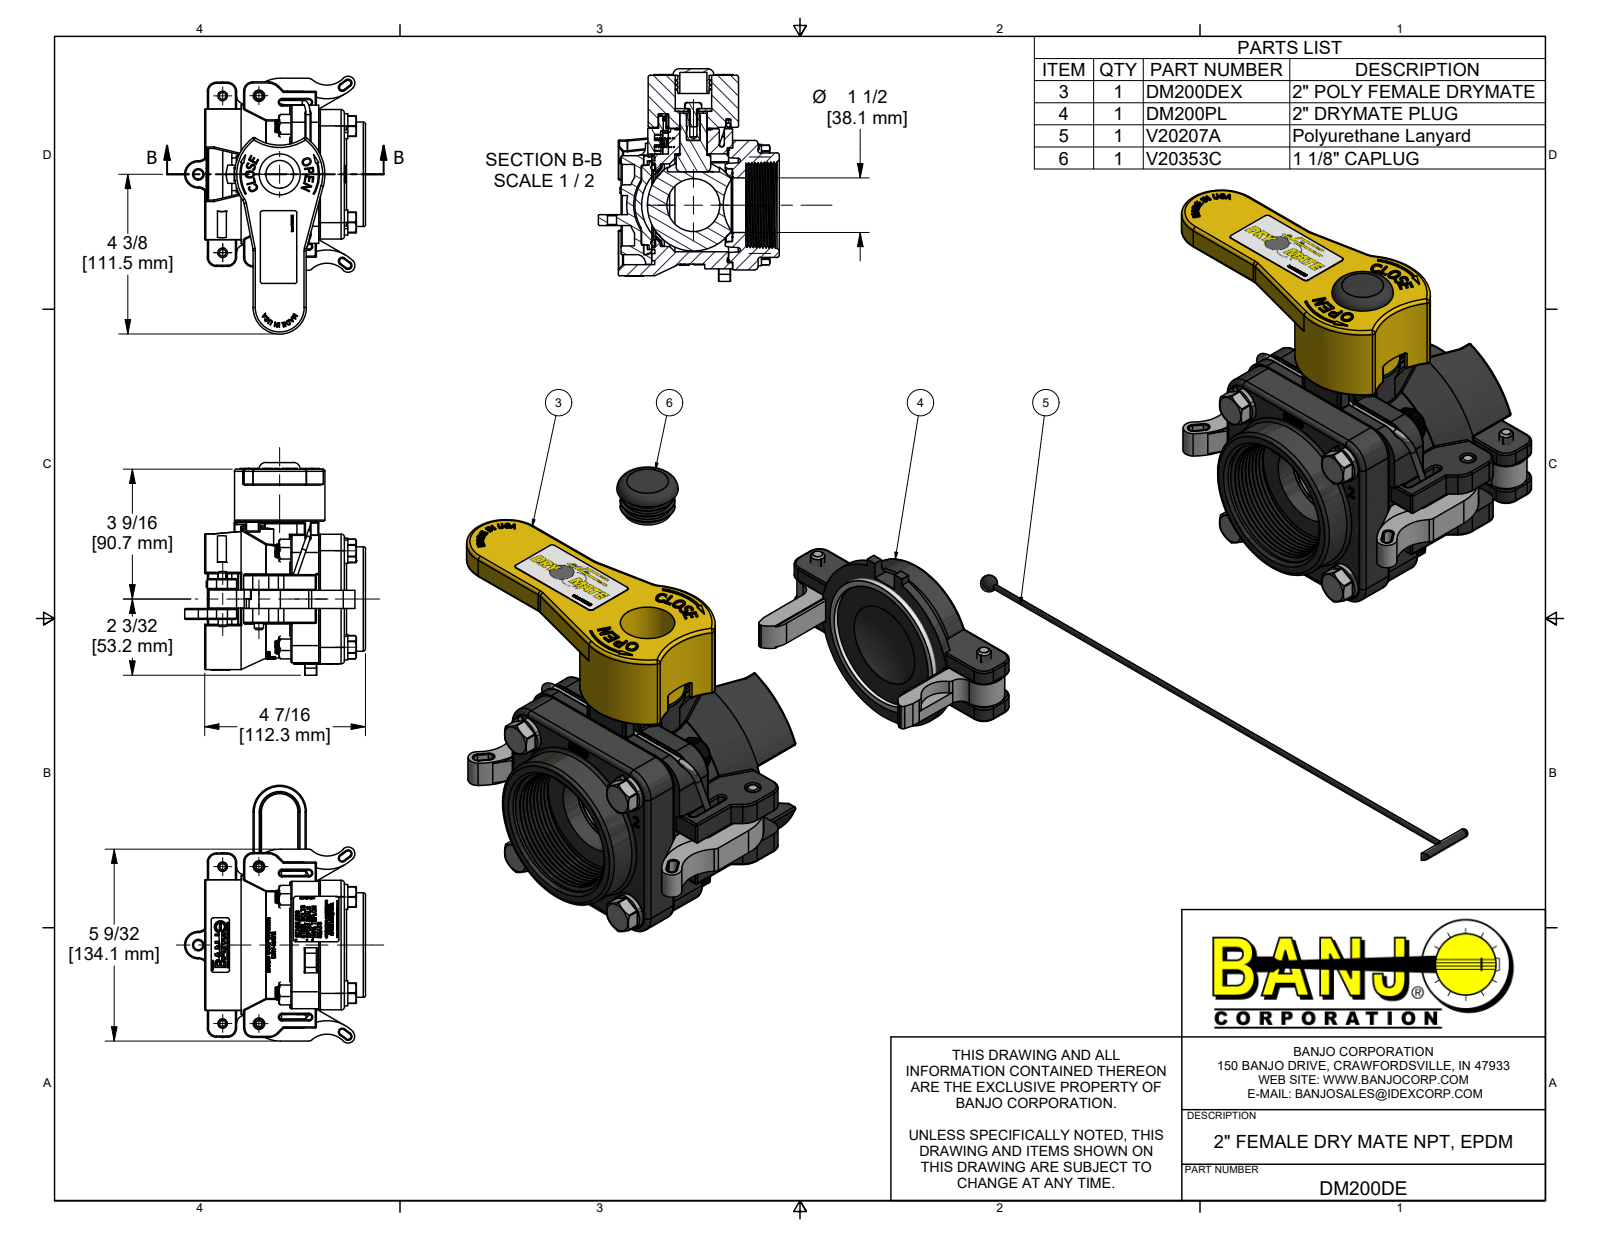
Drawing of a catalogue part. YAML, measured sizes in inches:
part_name: "DM200DE; DM200DEX; DM20254F; DM20254FY (+8 more)"
step_written_by: "Autodesk Inventor 2022 (AUTOMOTIVE_DESIGN)"
units: inches
bodies: {solids: 45, faces: 6625, planar: 3057, cylindrical: 1048, other: 2520}
overall_size: [7.084, 5.845, 4.972]
volume: 45.32
surface_area: 404.1
round_holes:
  - {diameter: 0.25, count: 5}
  - {diameter: 0.375, count: 5}
  - {diameter: 0.256, count: 4}
  - {diameter: 0.307, count: 4}
  - {diameter: 0.385, count: 4}
  - {diameter: 0.41, count: 4}
  - {diameter: 0.42, count: 4}
  - {diameter: 0.125, count: 3}
  - {diameter: 0.196, count: 1}
  - {diameter: 0.2, count: 1}
  - {diameter: 0.227, count: 1}
  - {diameter: 0.281, count: 1}
round_bosses_or_shafts:
  - {diameter: 0.324, count: 60}
  - {diameter: 0.12, count: 5}
  - {diameter: 0.687, count: 4}
  - {diameter: 0.375, count: 4}
  - {diameter: 0.26, count: 4}
  - {diameter: 0.249, count: 4}
  - {diameter: 0.28, count: 3}
  - {diameter: 3.25, count: 1}
partial_cylinders:
  - {radius: 0.03, count: 159}
  - {radius: 0.01, count: 41}
  - {radius: 0.06, count: 35}
  - {radius: 0.02, count: 20}
  - {radius: 0.25, count: 11}
  - {radius: 0.12, count: 10}
  - {radius: 0.08, count: 8}
  - {radius: 0.09, count: 8}
face_to_face_distances: [0.11, 0.298, 0.5, 0.013, 0.225, 3.833, 0.297, 0.822, 1.517, 0.92]
hole_center_spacings: [2.654, 1.872, 1.881, 2.648, 2.66, 3.753, 0.95, 0.986]
